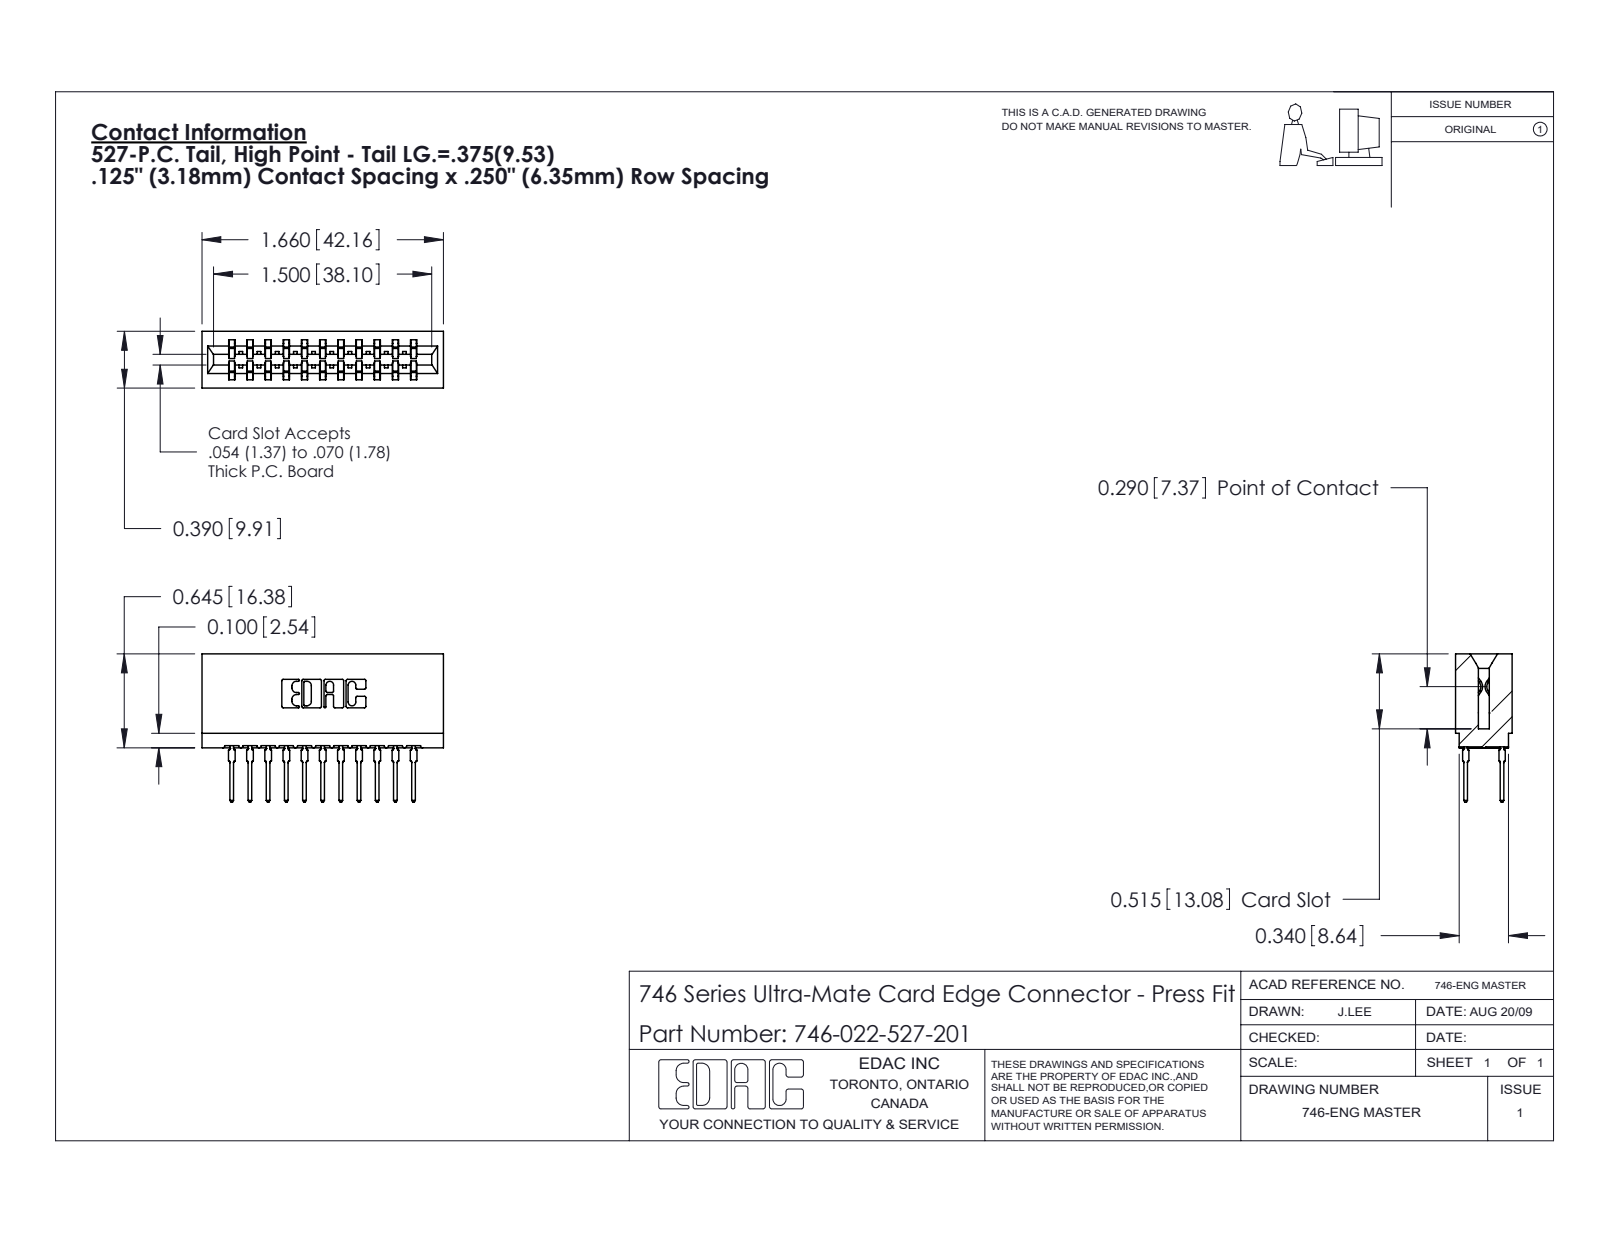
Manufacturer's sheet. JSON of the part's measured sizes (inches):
{"part_name": "746-292-001_527; 746-022-527-201; 746 Part_.515 Slot Depth - 01", "step_written_by": "SolidWorks 2020 (CONFIG_CONTROL_DESIGN)", "units": "inches", "bodies": {"solids": 23, "faces": 2066, "planar": 1067, "cylindrical": 427, "other": 572}, "overall_size": [1.66, 1.019, 0.39], "volume_in3": 0.29, "surface_area_in2": 11.14, "partial_cylinders_radius": [[0.021, 44], [0.01, 22], [0.015, 12], [0.005, 8], [0.011, 8], [0.007, 6], [0.031, 6], [0.026, 3]], "face_to_face_distances": [0.25, 0.333, 0.057, 0.5, 0.125, 0.125, 0.083, 0.39, 0.042, 0.208]}
